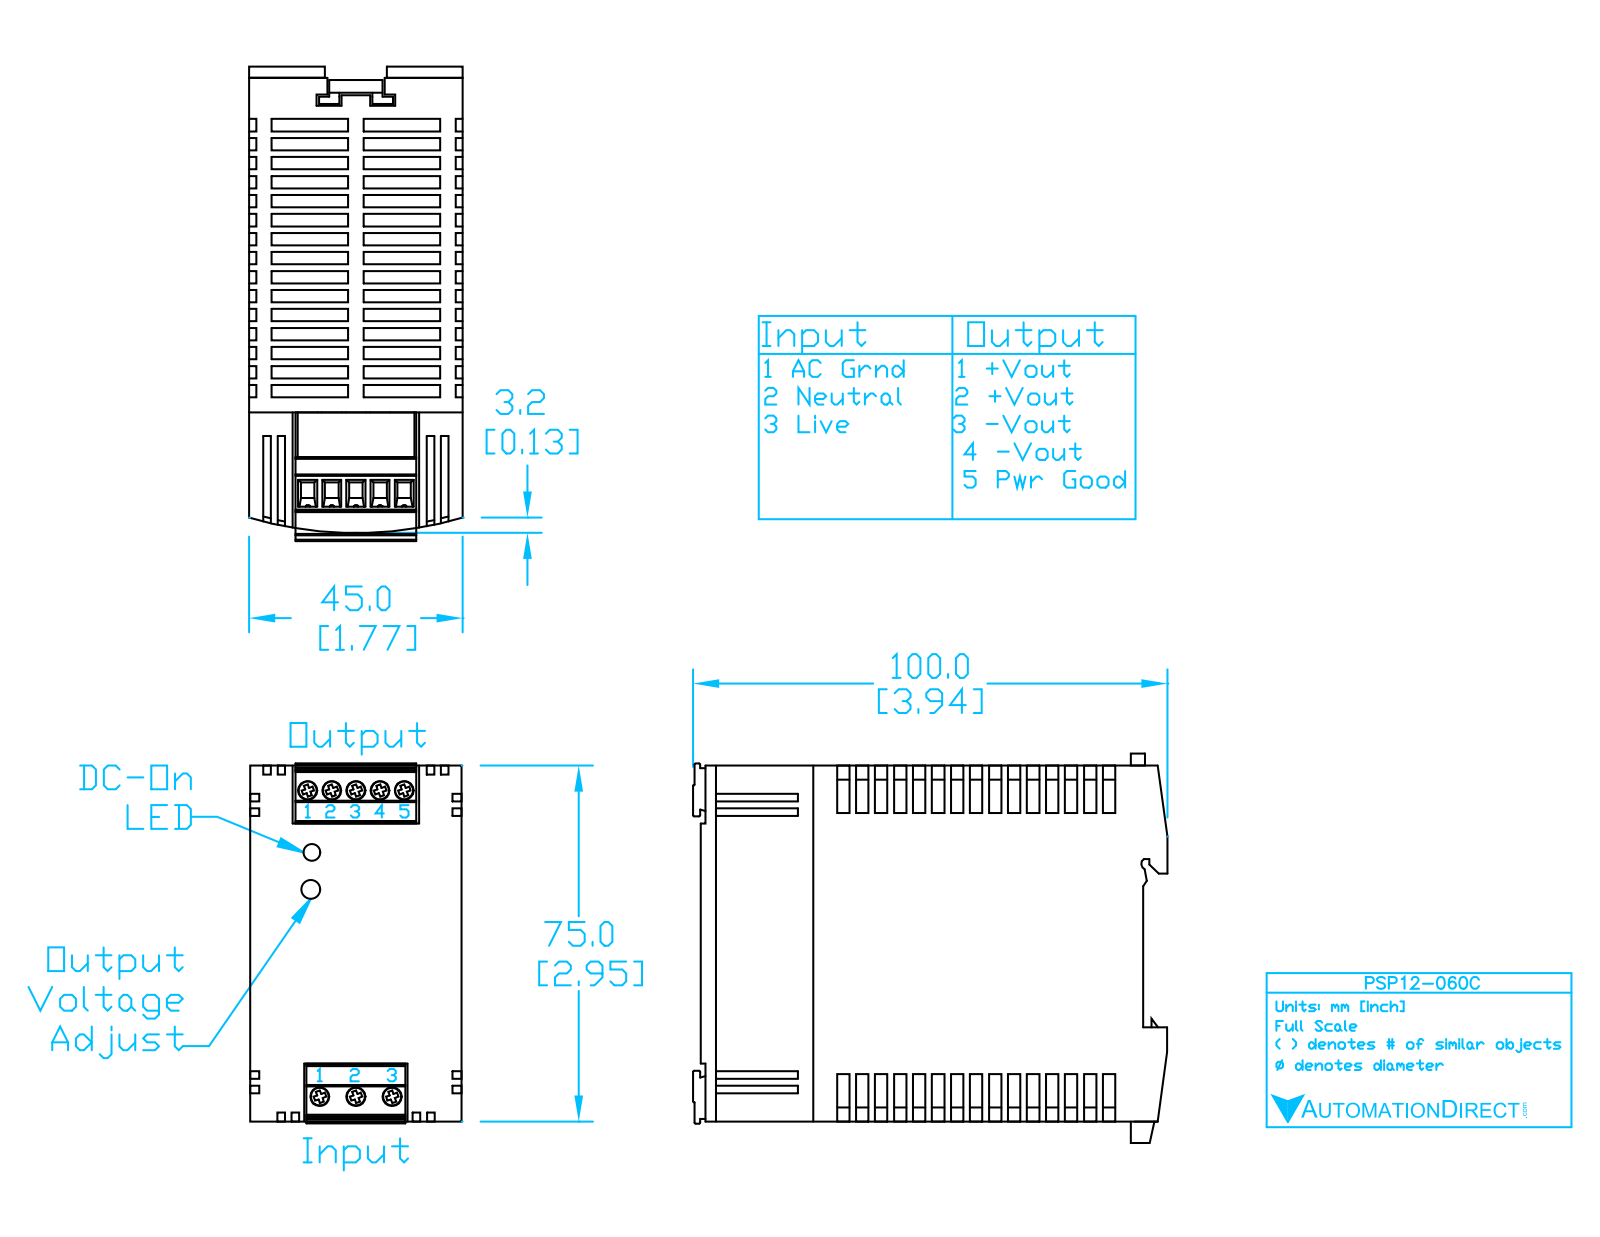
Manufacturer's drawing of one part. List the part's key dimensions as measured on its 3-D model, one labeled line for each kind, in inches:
Part name (STEP PRODUCT): PSP12-060C
STEP written by: SolidWorks 2011 (CONFIG_CONTROL_DESIGN)
Units: inches
Bodies: 3 solids, 485 faces (414 planar, 0 cylindrical, 71 other)
Overall size (bounding box): 3.948 × 3.15 × 1.772
Volume: 19.52 in³ · Surface area: 61.56 in²
Main face-to-face distances: 1.772, 2.953, 0.482, 2.47, 0.079, 0.067, 1.988, 0.082, 0.63, 2.789
